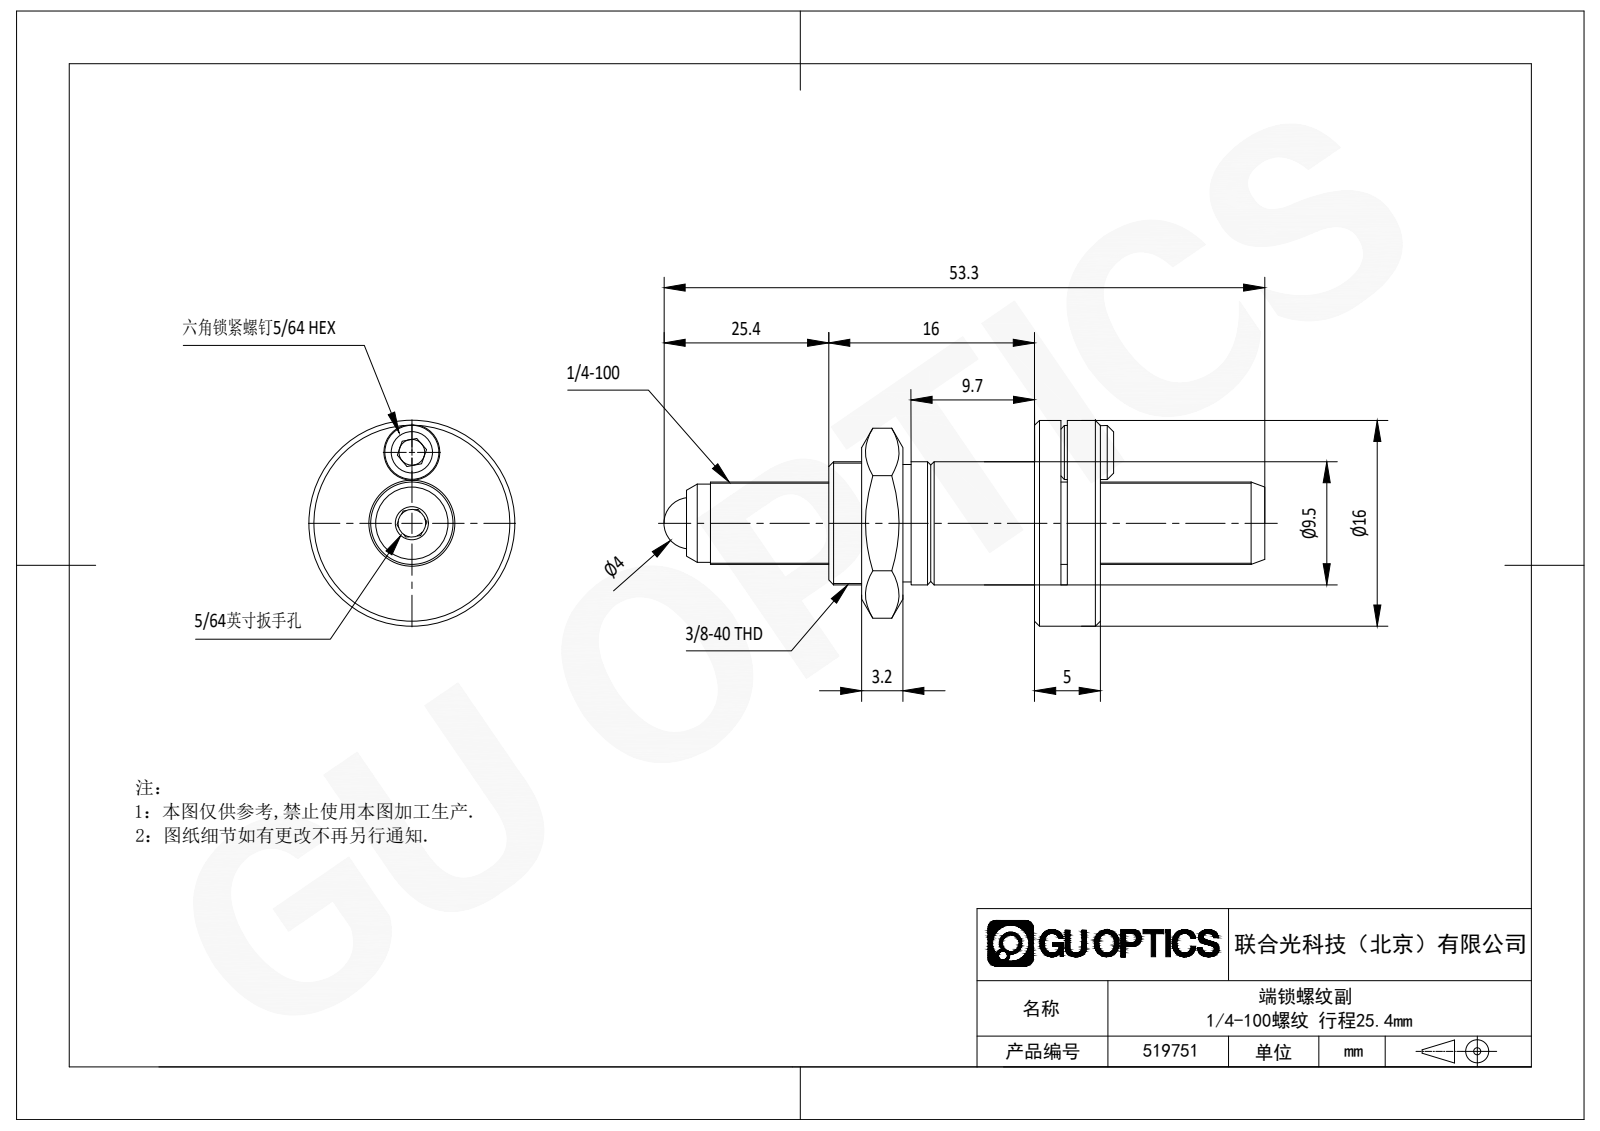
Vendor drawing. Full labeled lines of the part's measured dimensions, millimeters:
Part name (STEP PRODUCT): AJS100-1H
STEP written by: SolidWorks 2020 (CONFIG_CONTROL_DESIGN)
Units: millimetres
Bodies: 1 solid, 91 faces (48 planar, 17 cylindrical, 26 other)
Overall size (bounding box): 53.35 × 16 × 16
Volume: 3 177 mm³ · Surface area: 2 546 mm²
Round holes (diameter × count): ⌀1.5 ×1, ⌀2.12 ×1, ⌀6.6 ×1
Round bosses / shafts (diameter × count): ⌀16 ×1, ⌀9.52 ×1, ⌀9.5 ×1, ⌀8.74 ×1, ⌀6.35 ×1, ⌀4.17 ×1
Partial cylindrical surfaces — rounded edges, fillets, slot ends (radius × count): R7.56 ×1, R25.4 ×1
Main face-to-face distances: 0.51, 3.05, 2.54, 5, 2.46, 1.95, 12.7, 15.37, 15.24, 12.19
